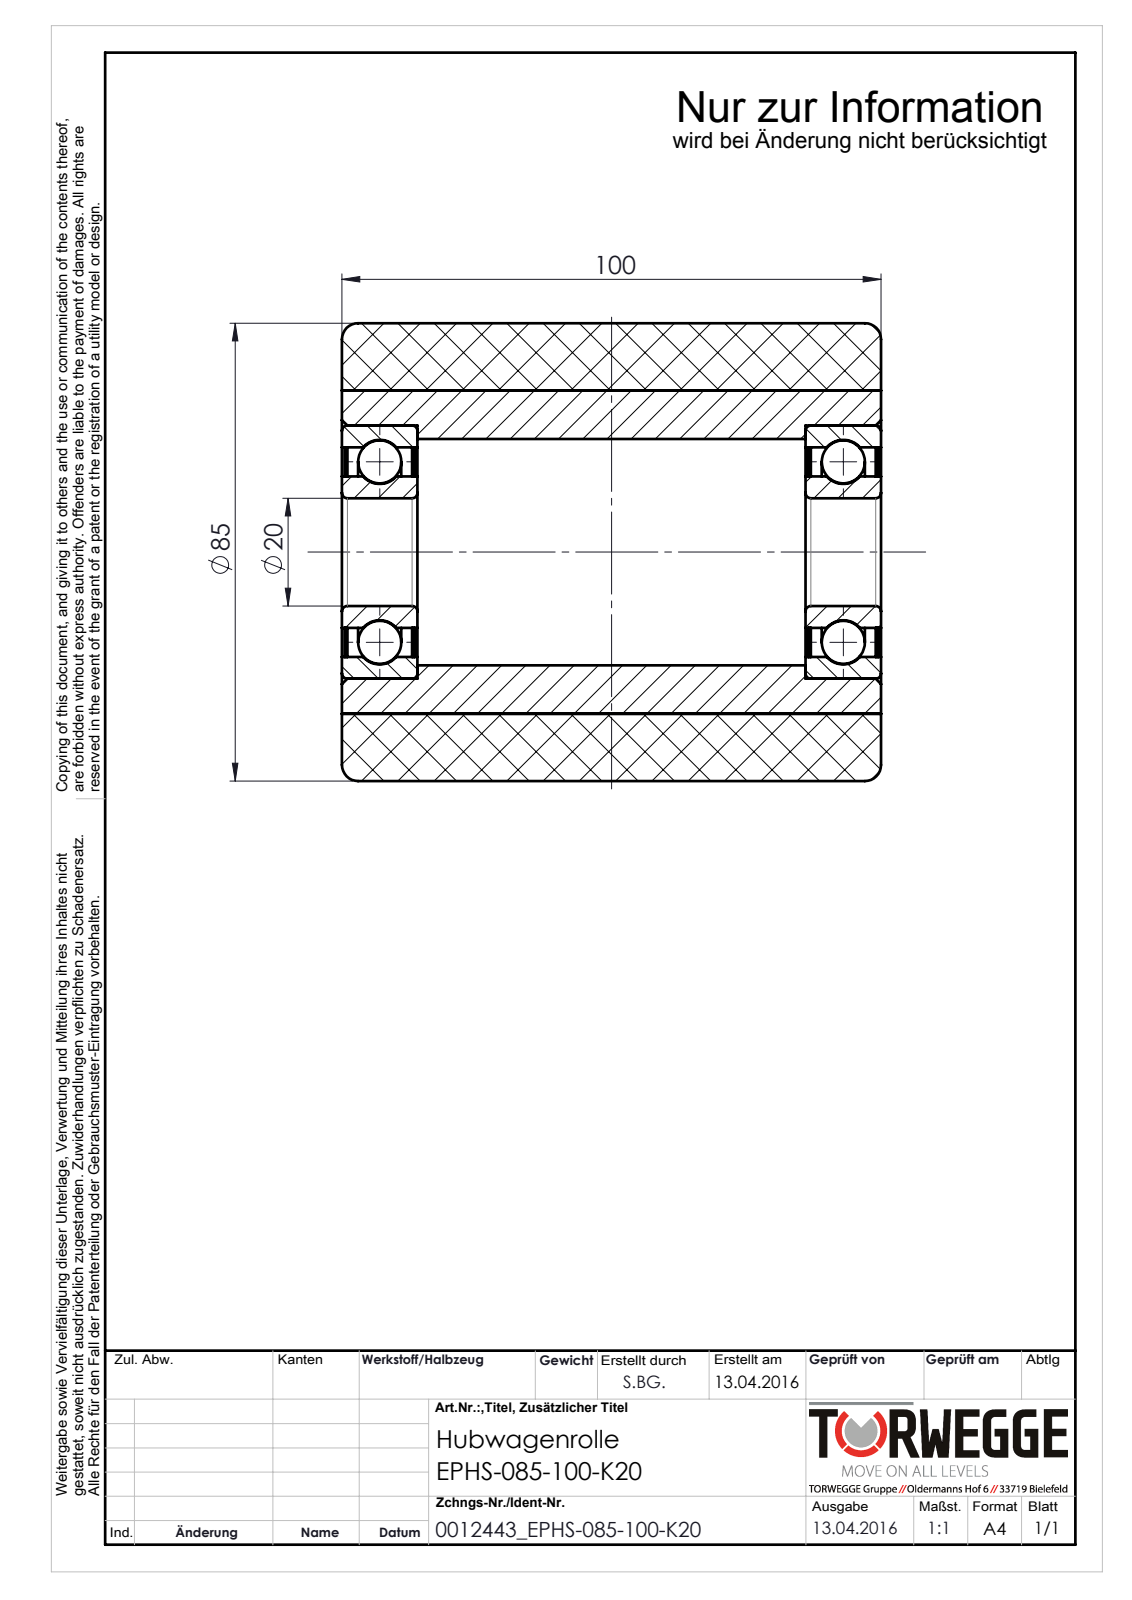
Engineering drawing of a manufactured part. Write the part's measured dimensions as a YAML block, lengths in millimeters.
part_name: "0012443_EPHS-085-100-K20"
step_written_by: "SolidWorks 2016 (AUTOMOTIVE_DESIGN)"
units: millimeters
bodies: {solids: 12, faces: 118, planar: 22, cylindrical: 52, other: 44}
overall_size: [100, 85, 85]
volume: 450839
surface_area: 111186
round_holes:
  - {diameter: 20, count: 1}
  - {diameter: 28.1, count: 1}
  - {diameter: 38.9, count: 1}
  - {diameter: 42, count: 1}
  - {diameter: 47, count: 1}
  - {diameter: 60, count: 1}
round_bosses_or_shafts:
  - {diameter: 85, count: 1}
face_to_face_distances: [0.5, 86, 100, 13, 1, 13.5, 86.5, 85.5, 12.5, 14]
